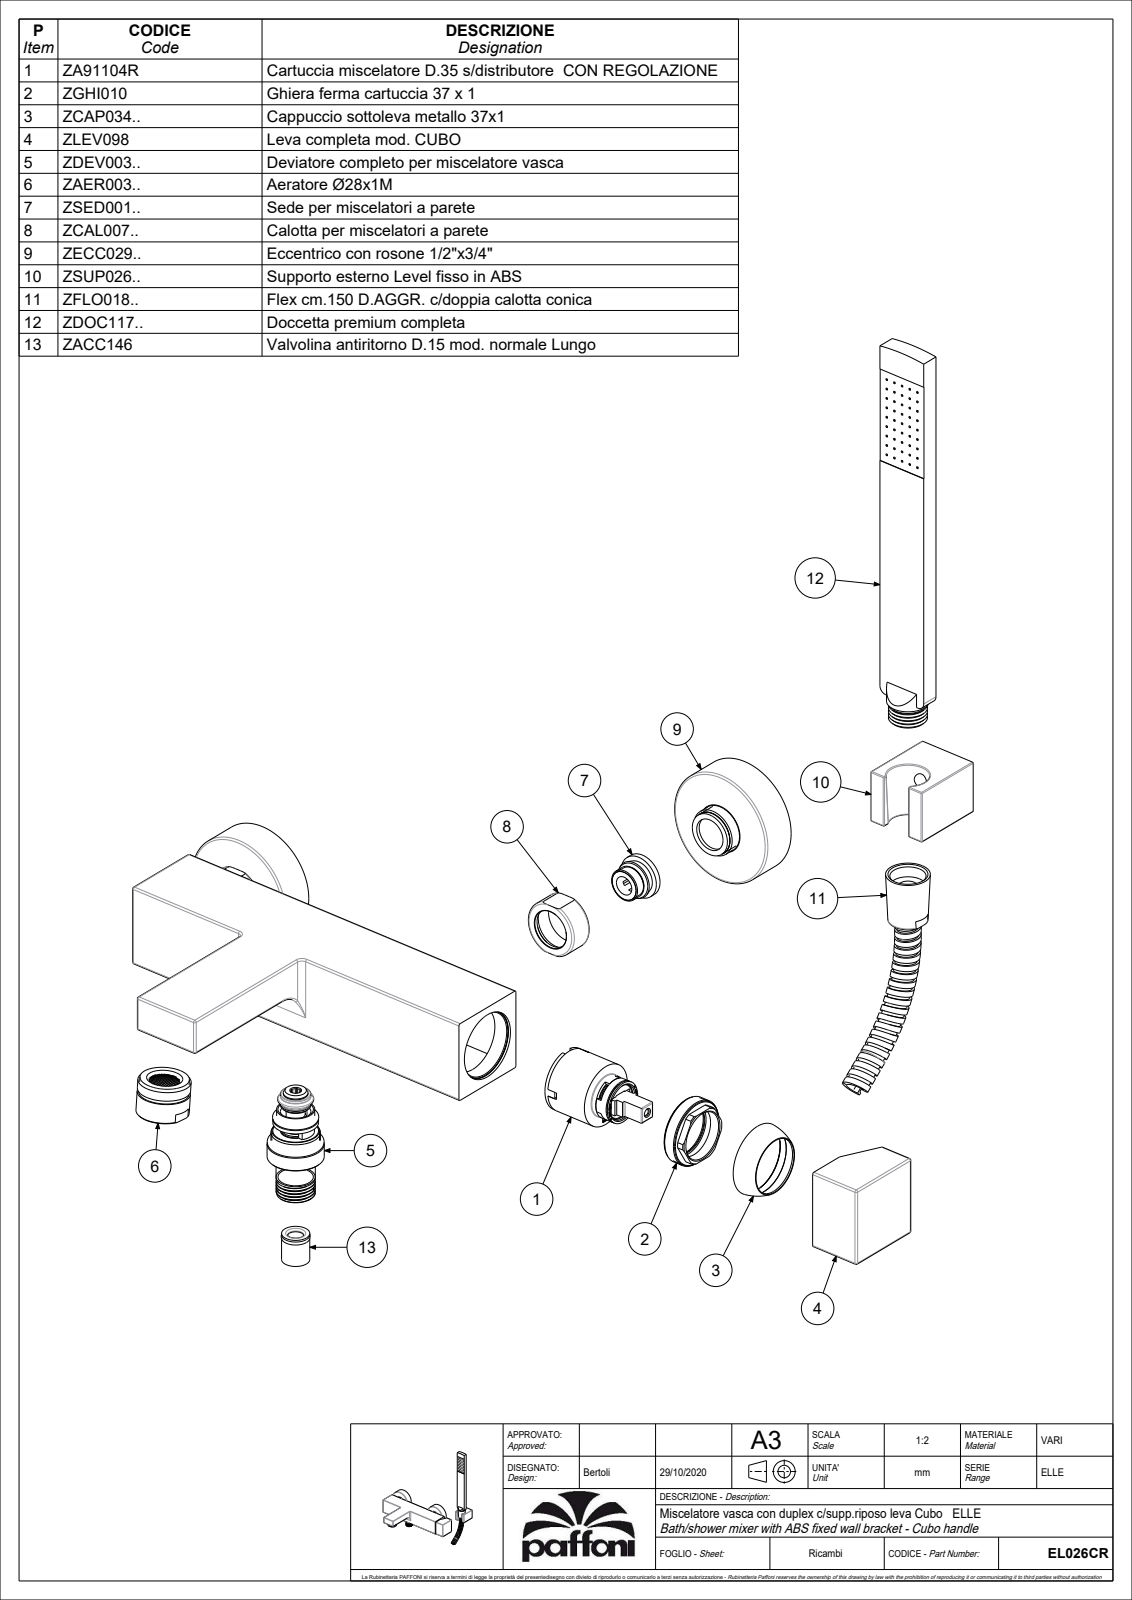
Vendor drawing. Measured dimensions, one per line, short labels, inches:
name: EL026CR
written by: CREO PARAMETRIC BY PTC INC, 2020044 (CONFIG_CONTROL_DESIGN)
unit: in
bodies: 5 solids, 328 faces (85 planar, 105 cylindrical, 138 other)
size: 15.089 × 14.734 × 6.624
volume: 45.11 in³; area: 240.8 in²
holes: 2× ⌀0.85, 2× ⌀0.965, 2× ⌀0.984, 2× ⌀2.453, 1× ⌀1.654
bosses: 2× ⌀2.5, 2× ⌀1.063, 1× ⌀1.102, 1× ⌀0.886, 1× ⌀0.811, 1× ⌀0.709, 1× ⌀0.591, 1× ⌀0.354
rounds: 24× R0.039, 14× R0.02, 3× R0.118, 2× R0.157, 2× R0.614, 1× R0.156, 1× R0.591, 1× R4.449
face distances: 1.831, 1.378, 3.209, 0.787, 1.079, 0.299, 2.13, 1.078, 1.377, 3.207
hole spacings: 5.906
